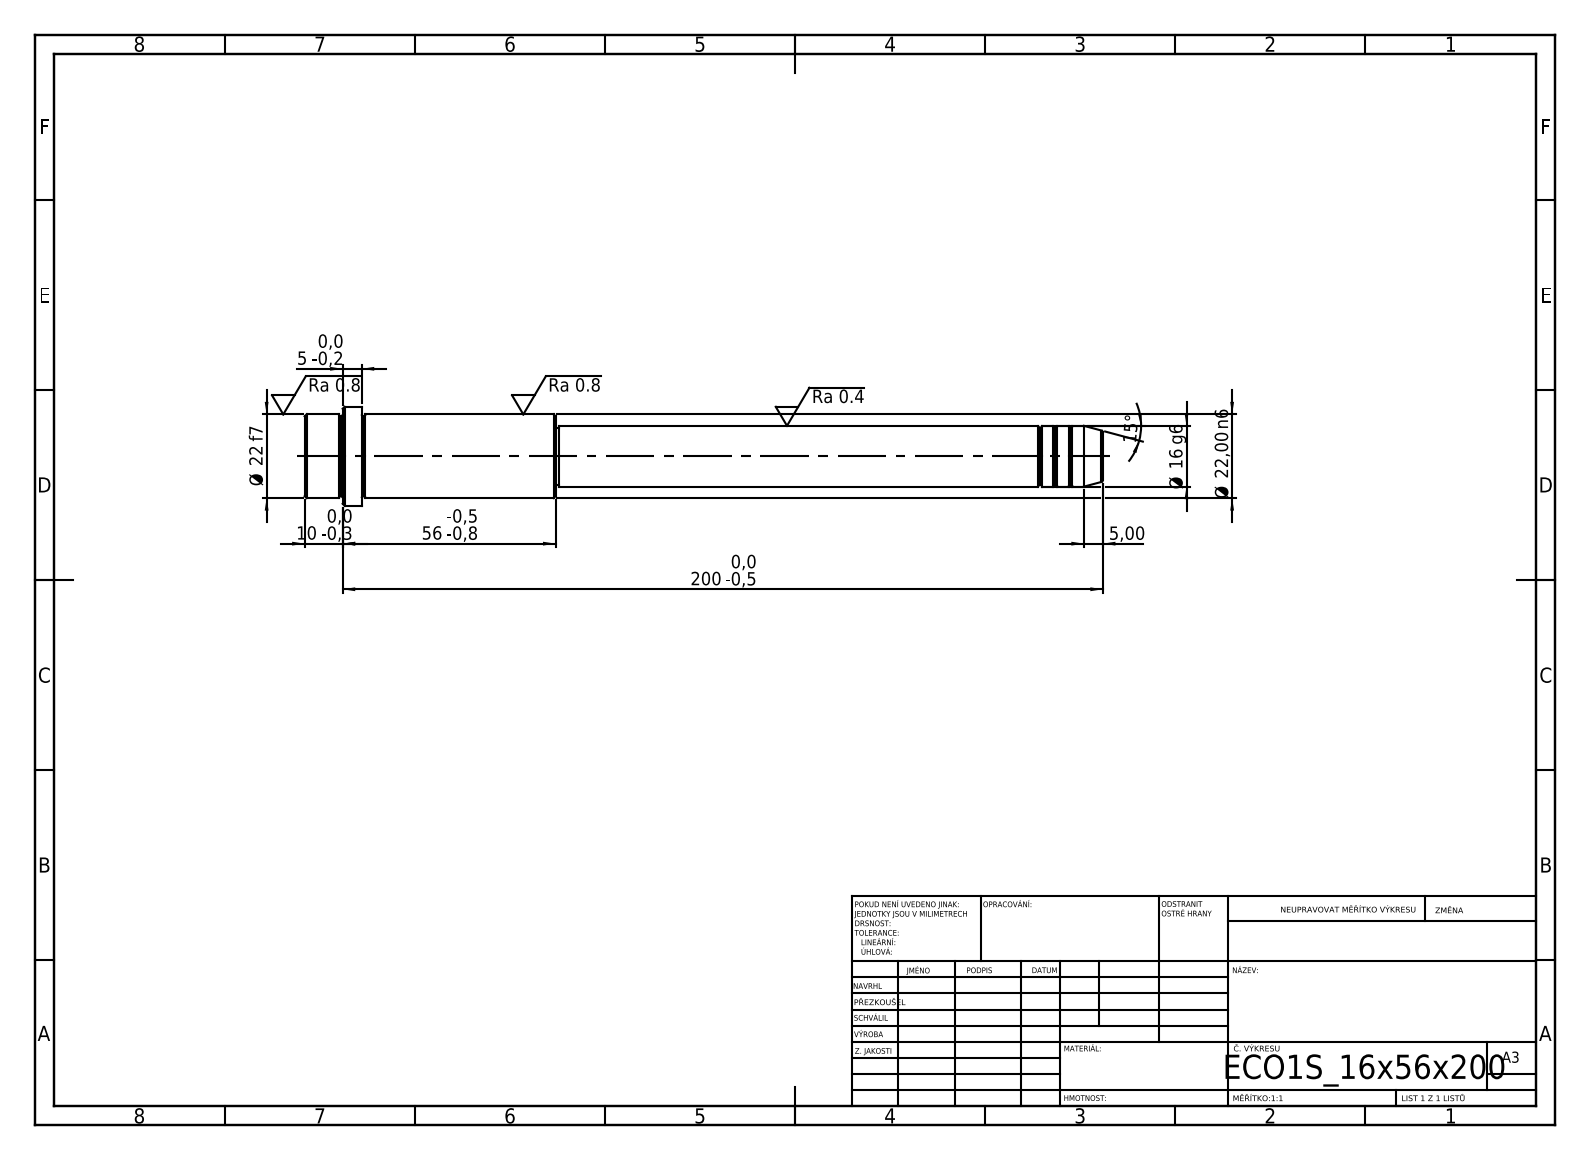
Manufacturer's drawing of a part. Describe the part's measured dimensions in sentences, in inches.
Its 3-D file was written by "SolidWorks 2019 (CONFIG_CONTROL_DESIGN)". It is 1 solid with 52 faces: 6 planar, 16 cylindrical and 30 other. Overall it measures 8.268 by 1.024 by 1.024 inches. Its volume is 3.324 cubic inches and its surface area 20.11 square inches. Round bosses or shafts: 1 of diameter 1.024, 1 of diameter 0.866, 1 of diameter 0.63, 1 of diameter 0.591. The main face-to-face distances are 2.598, 2.008, 0.591, 5.669, 7.677, 8.268, 7.874, 2.205, 0.197, 0.394.
